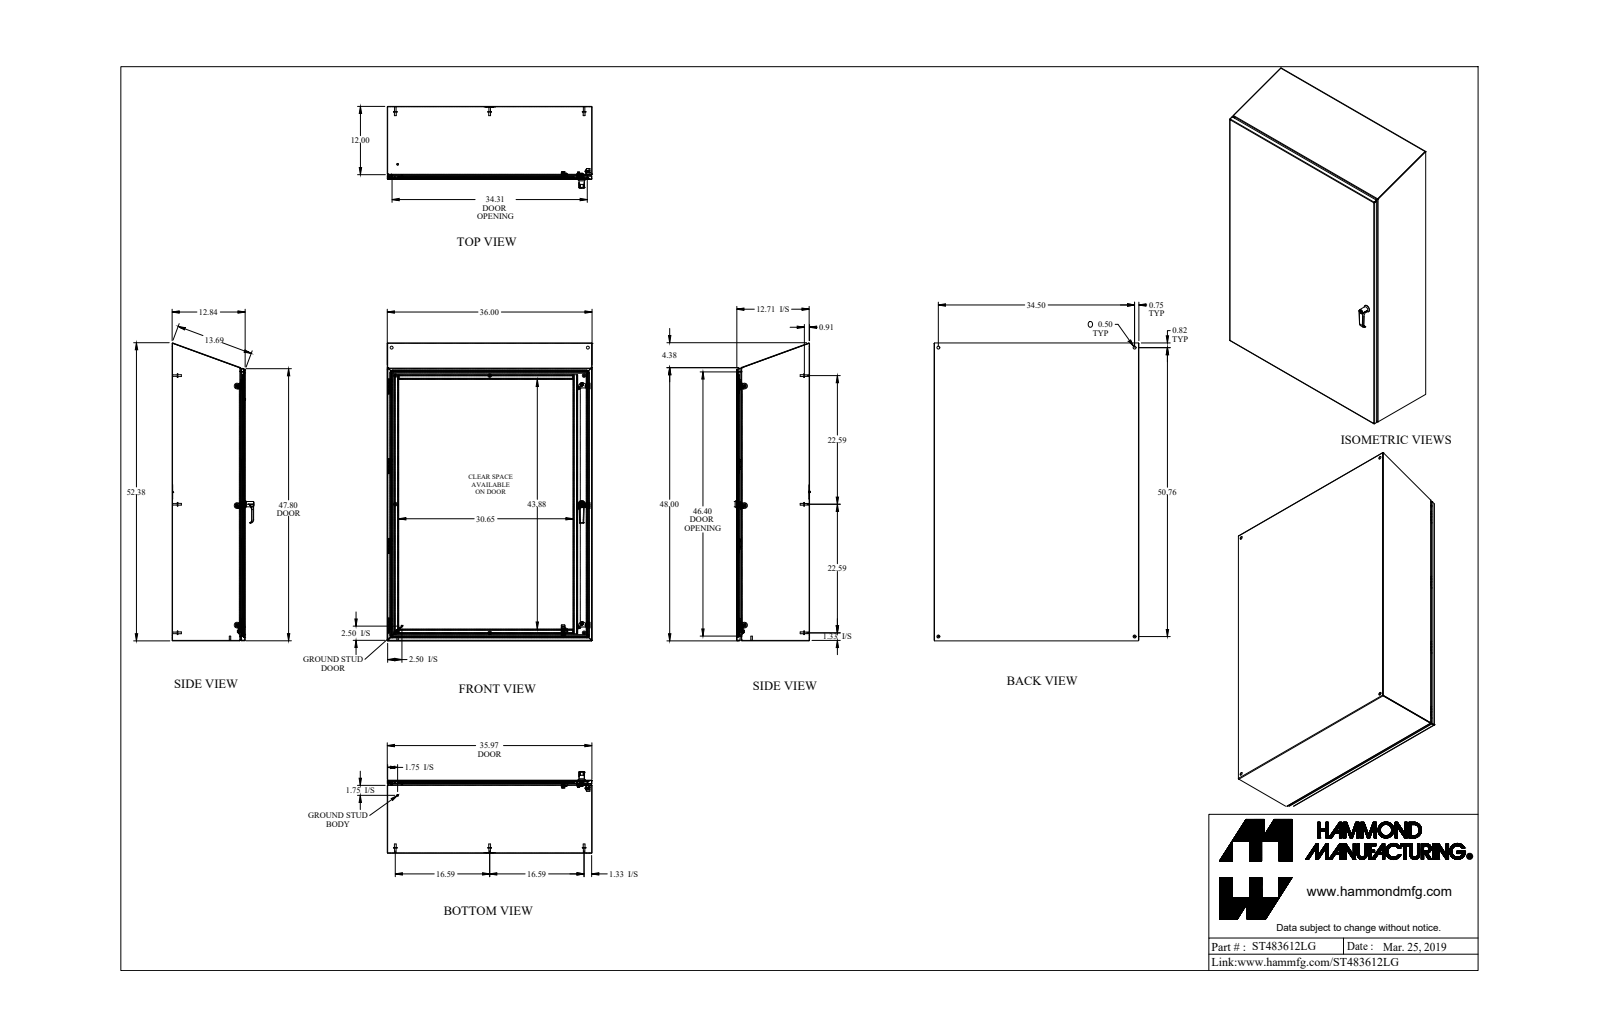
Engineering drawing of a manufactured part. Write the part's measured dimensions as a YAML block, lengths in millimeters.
part_name: "ST483612LG"
step_written_by: "SolidWorks 2018 (AUTOMOTIVE_DESIGN)"
units: millimeters
bodies: {solids: 64, faces: 1731, planar: 765, cylindrical: 643, other: 323}
overall_size: [1329.3, 914.4, 364.9]
volume: 7717000
surface_area: 8503000
round_holes:
  - {diameter: 4.5, count: 6}
  - {diameter: 5, count: 4}
  - {diameter: 12.7, count: 4}
  - {diameter: 6.4, count: 3}
  - {diameter: 6.7, count: 3}
  - {diameter: 10.5, count: 3}
  - {diameter: 6.5, count: 2}
  - {diameter: 8, count: 2}
  - {diameter: 10, count: 2}
  - {diameter: 4.4, count: 1}
  - {diameter: 6.1, count: 1}
  - {diameter: 6.1, count: 1}
round_bosses_or_shafts:
  - {diameter: 8, count: 9}
  - {diameter: 6.9, count: 9}
  - {diameter: 15.9, count: 7}
  - {diameter: 6.4, count: 7}
  - {diameter: 9.5, count: 6}
  - {diameter: 4, count: 6}
  - {diameter: 25.4, count: 3}
  - {diameter: 15.9, count: 3}
partial_cylinders:
  - {radius: 1.1, count: 24}
  - {radius: 2.1, count: 24}
  - {radius: 0.9, count: 19}
  - {radius: 2.7, count: 18}
  - {radius: 1.6, count: 17}
  - {radius: 0.8, count: 15}
  - {radius: 2.4, count: 10}
  - {radius: 0.4, count: 9}
face_to_face_distances: [1.8, 324.2, 322.4, 326.1, 912.6, 910.7, 914.4, 303, 21.3, 1]
hole_center_spacings: [533.4, 1066.8, 20, 519.4, 547.8, 876.3, 1289.4, 1559]
